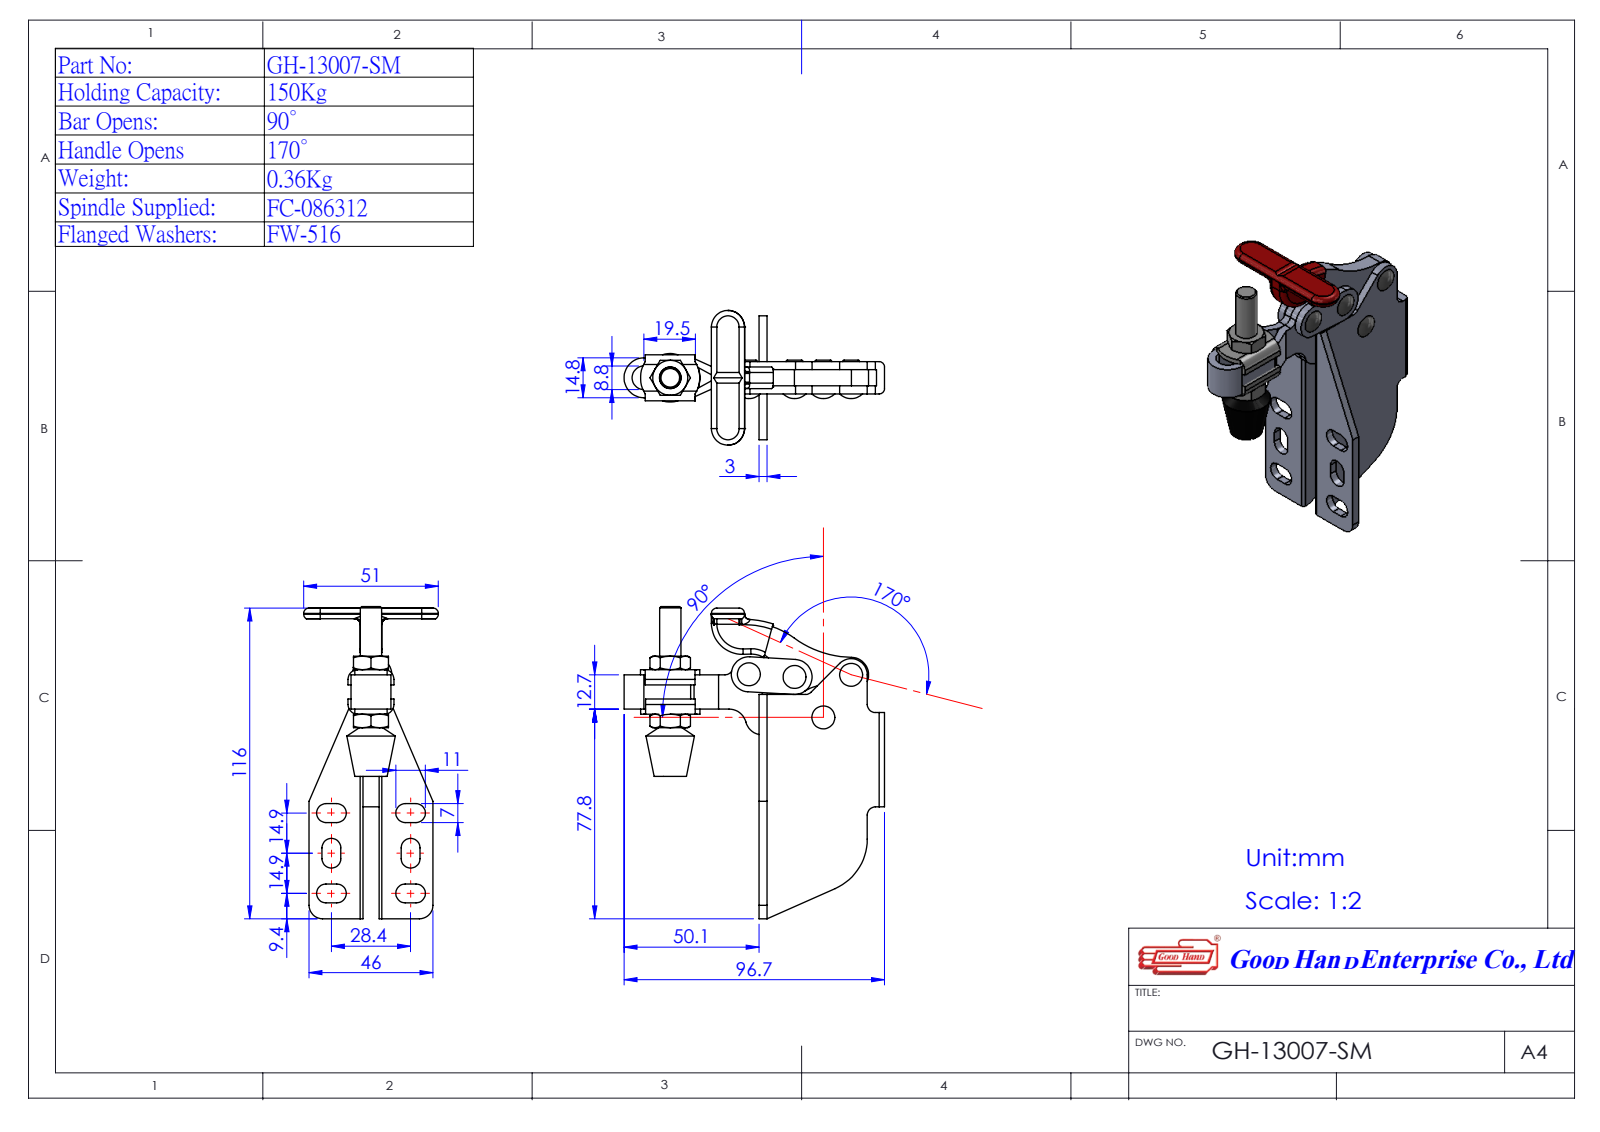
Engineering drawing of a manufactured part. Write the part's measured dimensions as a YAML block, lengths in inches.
part_name: "Group4^GH-13007-SM(簡化)-1; GH-13007-SM(簡化)-1; Group7^GH-13007-SM(簡化)-1; Group5^GH-13007-SM(簡化)-1 (+2 more)"
step_written_by: "SolidWorks 2016 (AUTOMOTIVE_DESIGN)"
units: inches
bodies: {solids: 5, faces: 422, planar: 219, cylindrical: 153, other: 50}
overall_size: [4.579, 3.807, 1.969]
volume: 3.109
surface_area: 60.02
round_holes:
  - {diameter: 0.157, count: 4}
  - {diameter: 0.189, count: 1}
  - {diameter: 0.19, count: 1}
round_bosses_or_shafts:
  - {diameter: 0.312, count: 1}
  - {diameter: 0.203, count: 1}
  - {diameter: 0.189, count: 1}
partial_cylinders:
  - {radius: 0.138, count: 12}
  - {radius: 0.118, count: 7}
  - {radius: 0.256, count: 6}
  - {radius: 0.047, count: 4}
  - {radius: 0.142, count: 4}
  - {radius: 0.197, count: 4}
  - {radius: 0.435, count: 3}
  - {radius: 0.039, count: 2}
face_to_face_distances: [0.118, 0.236, 0.354, 0.472, 0.039, 0.039, 0.157, 0.055, 0.173, 0.291]
hole_center_spacings: [0.669, 0.725, 0.743, 0.827, 1.256, 1.495]
